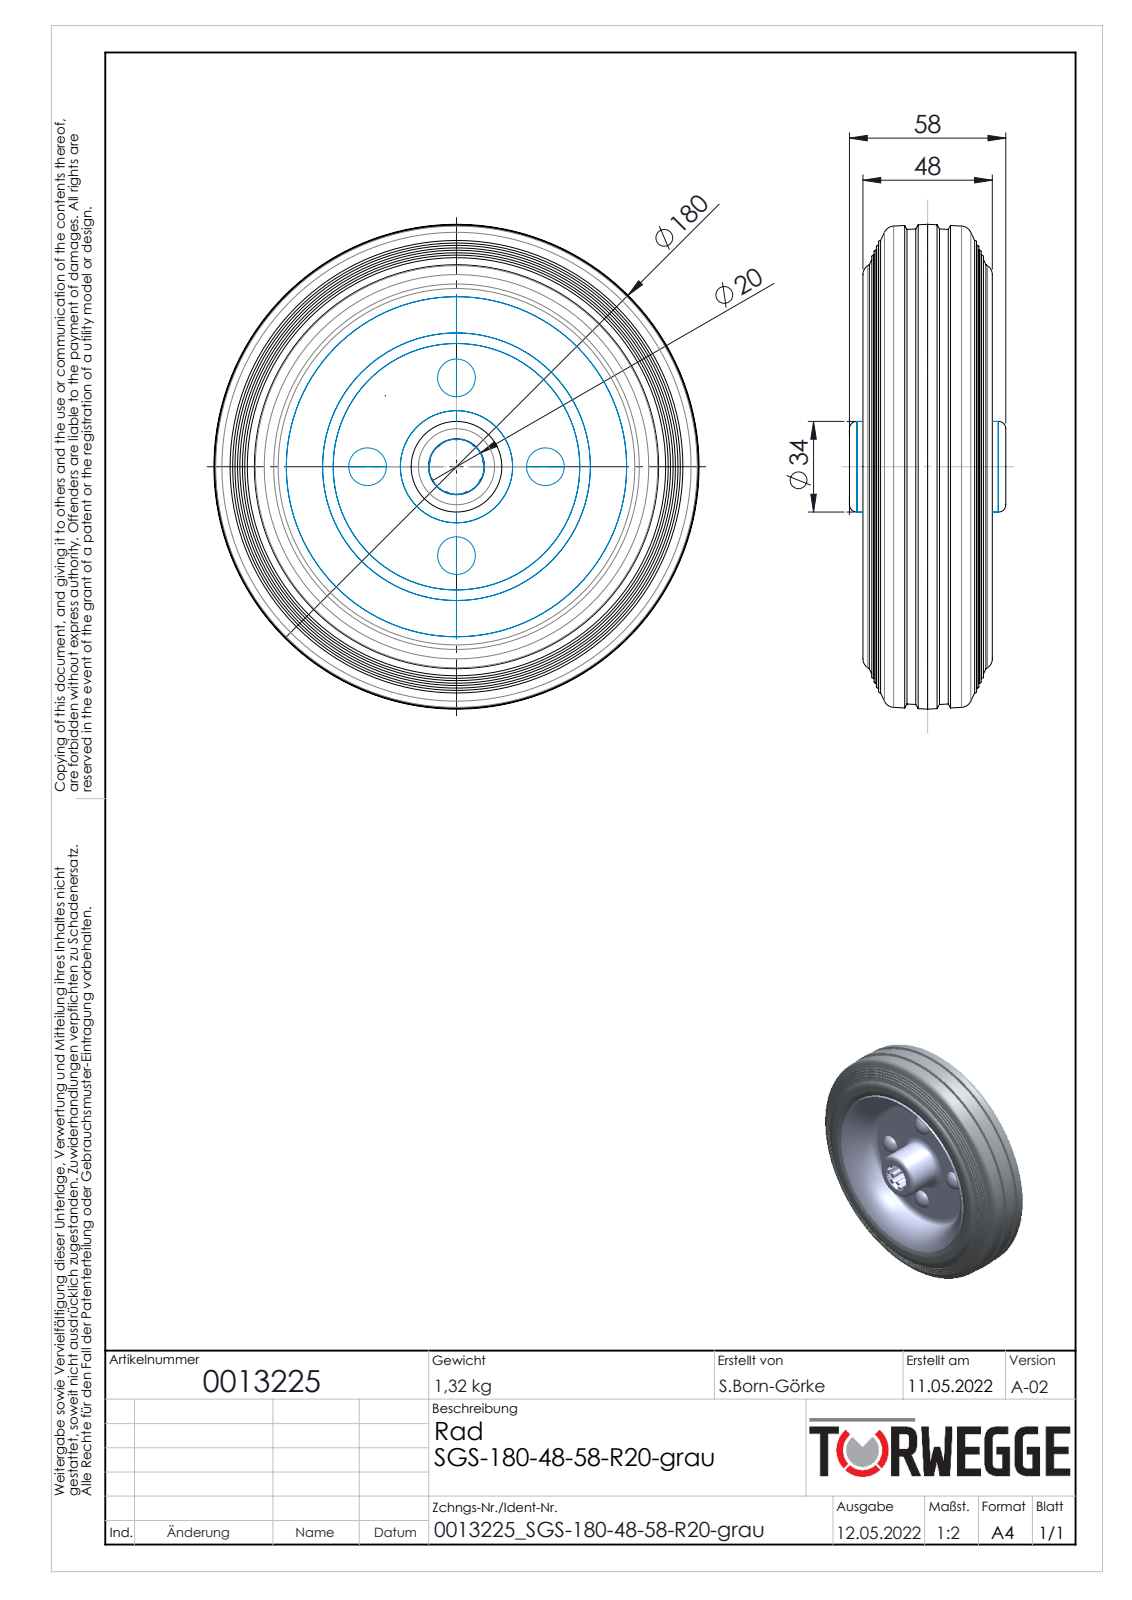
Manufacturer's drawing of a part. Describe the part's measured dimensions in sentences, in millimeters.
The part is named "0013225". Its 3-D file was written by "SolidWorks 2020 (AUTOMOTIVE_DESIGN)". It is 0 solids with 251 faces: 78 planar, 55 cylindrical and 118 other. Overall it measures 180 by 180 by 58 millimeters. Round holes: 1 of diameter 20.8. Round bosses or shafts: 1 of diameter 33.65, 1 of diameter 30.05, 1 of diameter 20.5. Partial cylindrical surfaces (rounded edges, fillets, slot ends): 9 of radius 2.5, 1 of radius 12.75. The main face-to-face distances are 3.6, 22.2, 25.8, 48, 3.45, 3, 52, 5, 27.2, 30.8.
